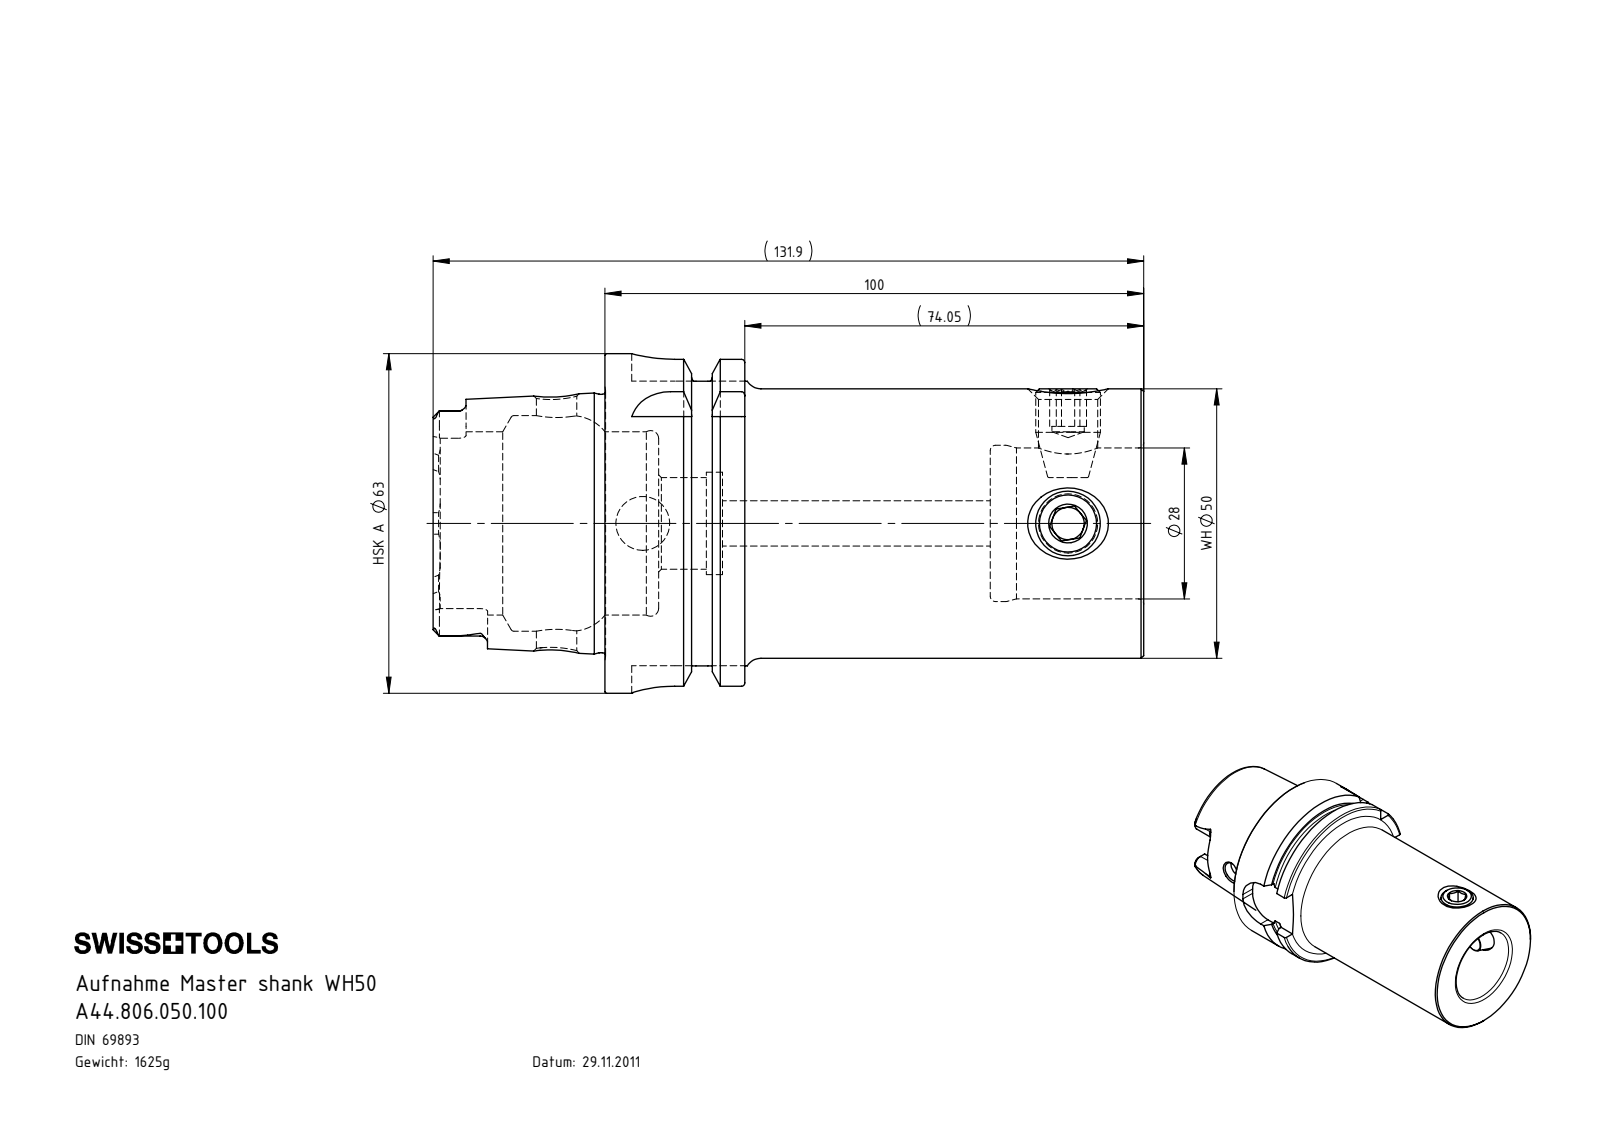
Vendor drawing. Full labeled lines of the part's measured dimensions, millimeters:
Part name (STEP PRODUCT): A44.806.050.100; WH5-ER1.001.017; HA6-WH5.K01.100_B
STEP written by: SolidWorks 2017 (CONFIG_CONTROL_DESIGN)
Units: millimetres
Bodies: 3 solids, 242 faces (76 planar, 61 cylindrical, 105 other)
Overall size (bounding box): 131.9 × 63 × 63
Volume: 207 026 mm³ · Surface area: 39 373 mm²
Round holes (diameter × count): ⌀6 ×2, ⌀11 ×2, ⌀7.5 ×1, ⌀8.4 ×1, ⌀10 ×1, ⌀17 ×1, ⌀19 ×1, ⌀28 ×1, ⌀29 ×1, ⌀34 ×1, ⌀40 ×1
Round bosses / shafts (diameter × count): ⌀12 ×2, ⌀63 ×1, ⌀54.95 ×1, ⌀50 ×1, ⌀47.94 ×1
Partial cylindrical surfaces — rounded edges, fillets, slot ends (radius × count): R1.4 ×6, R2.88 ×4, R8 ×4
Main face-to-face distances: 100, 9.95, 90.05, 71.5, 61.55, 28.5, 16, 25.95, 45.55, 74.05
Hole centre spacings: 78.95, 94.95
